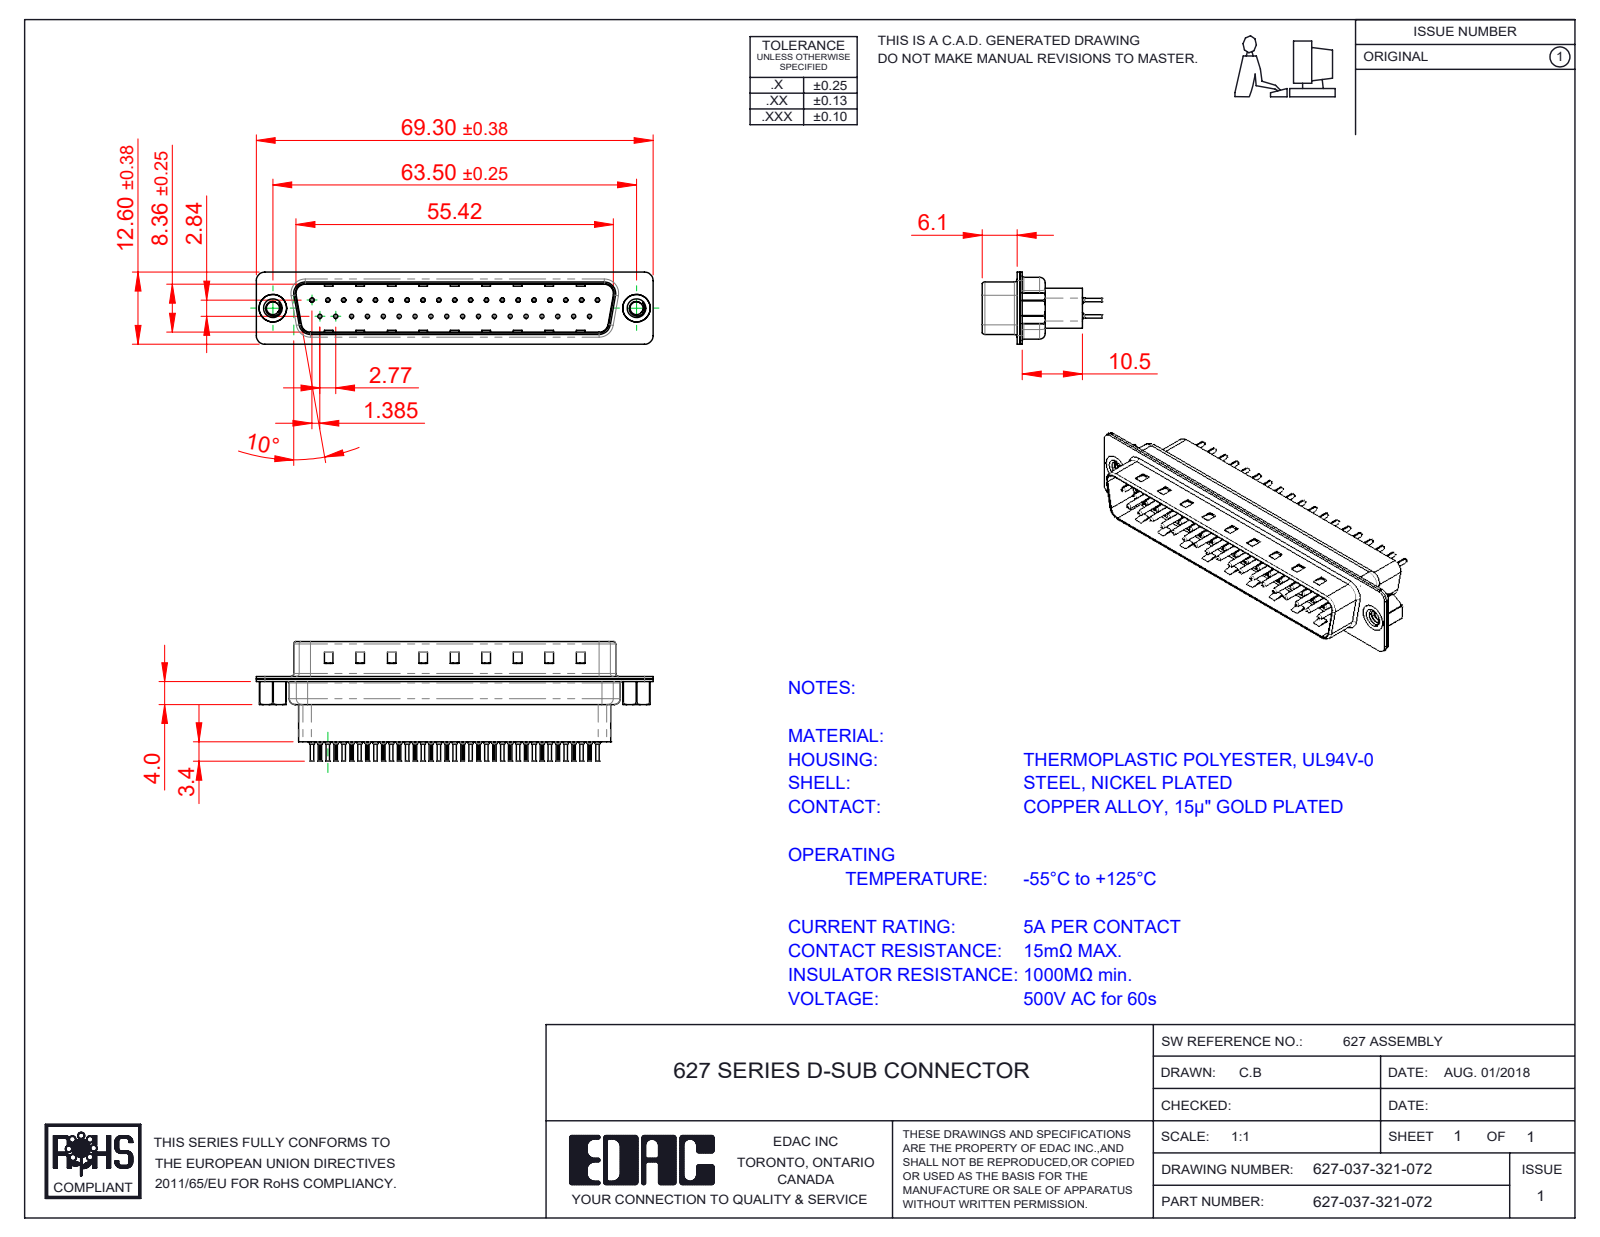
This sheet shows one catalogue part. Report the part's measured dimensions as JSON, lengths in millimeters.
{"part_name": "627 Contact Row 1_21H; 627-037-321-072; 627 Housing_37 HP; 627 4-40 Threaded Rivet (+3 more)", "step_written_by": "SolidWorks 2020 (CONFIG_CONTROL_DESIGN)", "units": "millimeters", "bodies": {"solids": 42, "faces": 4034, "planar": 1091, "cylindrical": 1508, "other": 1435}, "overall_size": [69.3, 20.8, 12.6], "volume_mm3": 5302, "surface_area_mm2": 13549, "round_holes": [[0.2, 37], [0.35, 37], [1.1, 37], [1.6, 37], [2.26, 2], [4, 2], [4.8, 2]], "round_bosses_or_shafts": [[2, 37], [1.5, 37], [0.75, 37], [0.6, 37], [5, 2], [4.9, 2]], "partial_cylinders_radius": [[0.1, 74], [1.5, 16], [2, 12], [0.5, 8], [1.6, 8], [0.25, 4], [0.6, 4], [0.65, 4]], "face_to_face_distances": [0.4, 0.82, 9.58, 0.68, 7.68, 0.45, 1.5, 1.08, 8.08, 8.76], "hole_center_spacings": [3.16, 2.77, 5.54, 8.31, 5.04, 10.1, 11.08, 12.78]}
